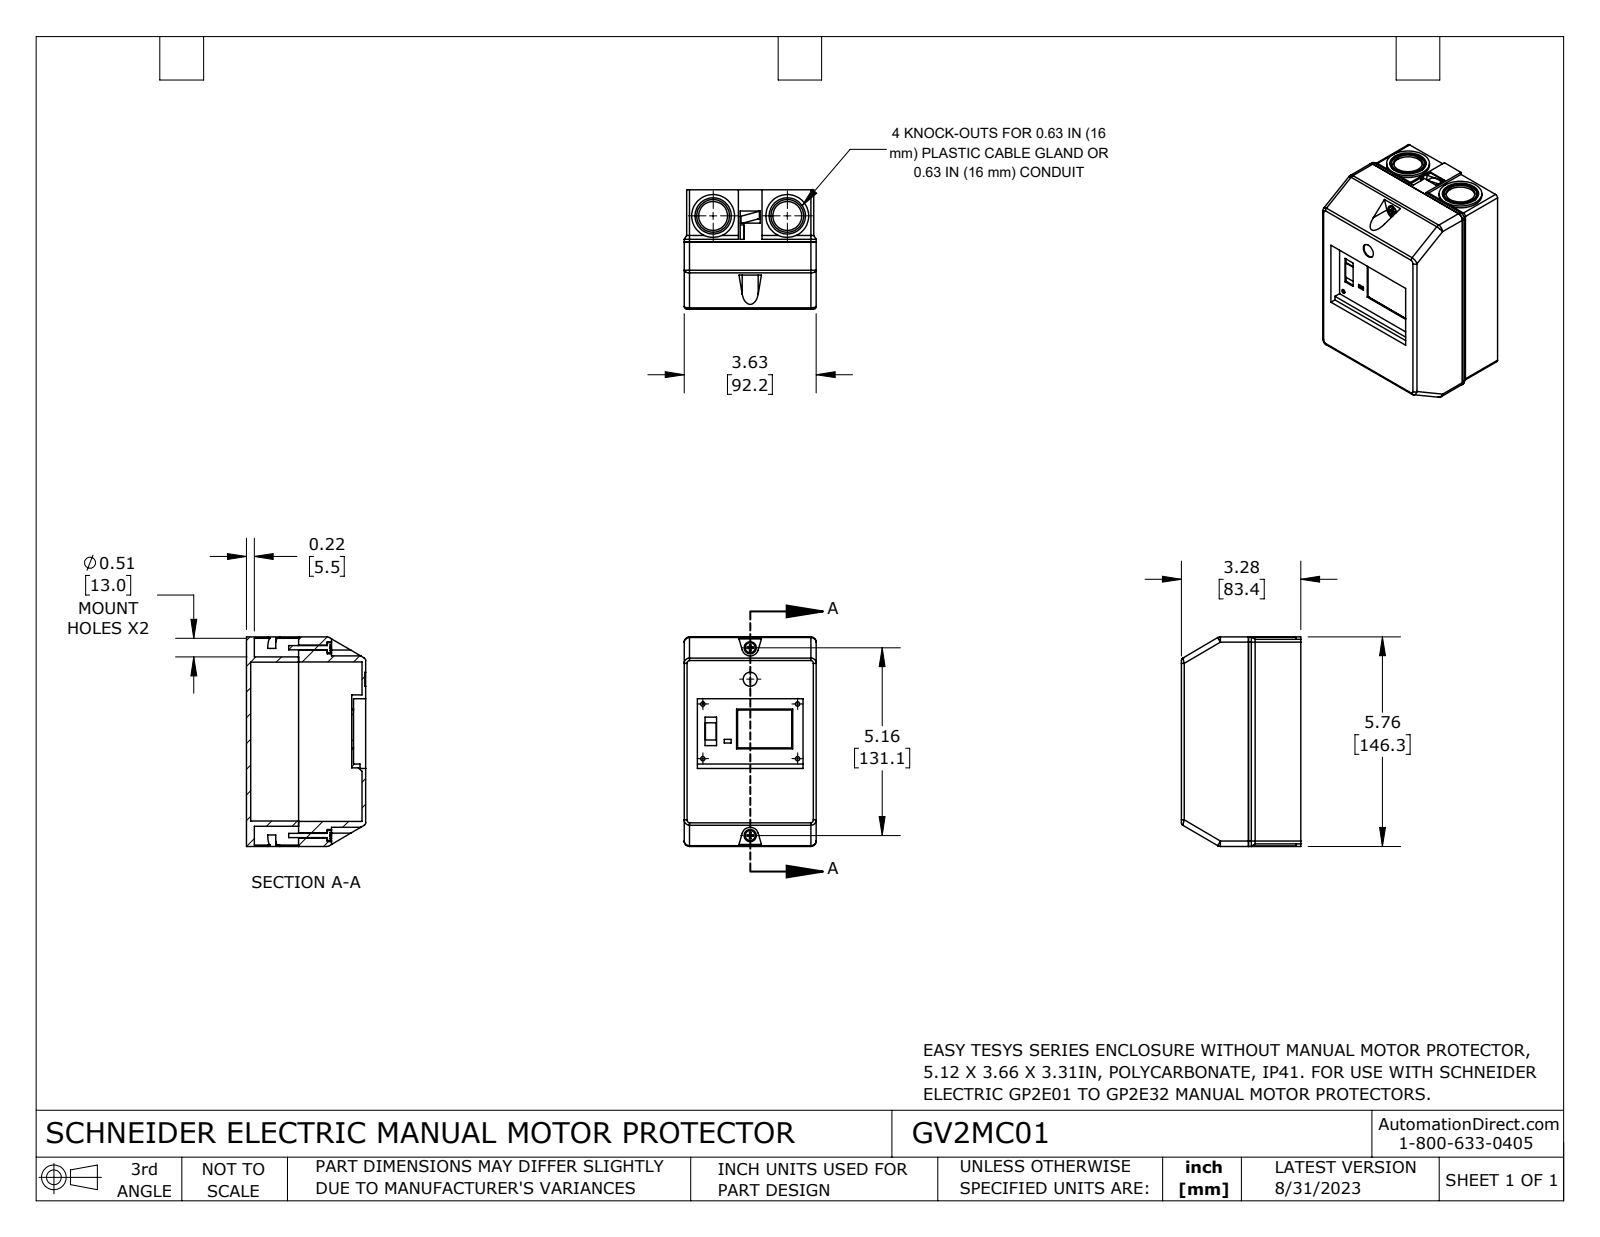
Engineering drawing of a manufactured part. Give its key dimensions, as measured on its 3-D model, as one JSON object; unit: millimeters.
{"part_name": "GV2MC01", "step_written_by": "SolidWorks 2021 (CONFIG_CONTROL_DESIGN)", "units": "millimeters", "bodies": {"solids": 4, "faces": 283, "planar": 173, "cylindrical": 94, "other": 16}, "overall_size": [146.3, 92.2, 83.3], "volume_mm3": 246800, "surface_area_mm2": 132100, "round_holes": [[3, 4], [3.5, 2], [8.5, 2], [13, 2], [20.1, 2], [25.3, 2], [9.8, 1]], "round_bosses_or_shafts": [[29.9, 2], [22.9, 2], [6.9, 2], [2.9, 2]], "partial_cylinders_radius": [[3.8, 10], [2, 8], [5.7, 2], [10.2, 2]], "face_to_face_distances": [2.6, 3.7, 1.8, 2, 3, 88.5, 89.6, 1.1, 85.9, 90.4], "hole_center_spacings": [37.4, 38.2, 51.4, 51.5, 63, 63.1, 64.6, 66.2]}
